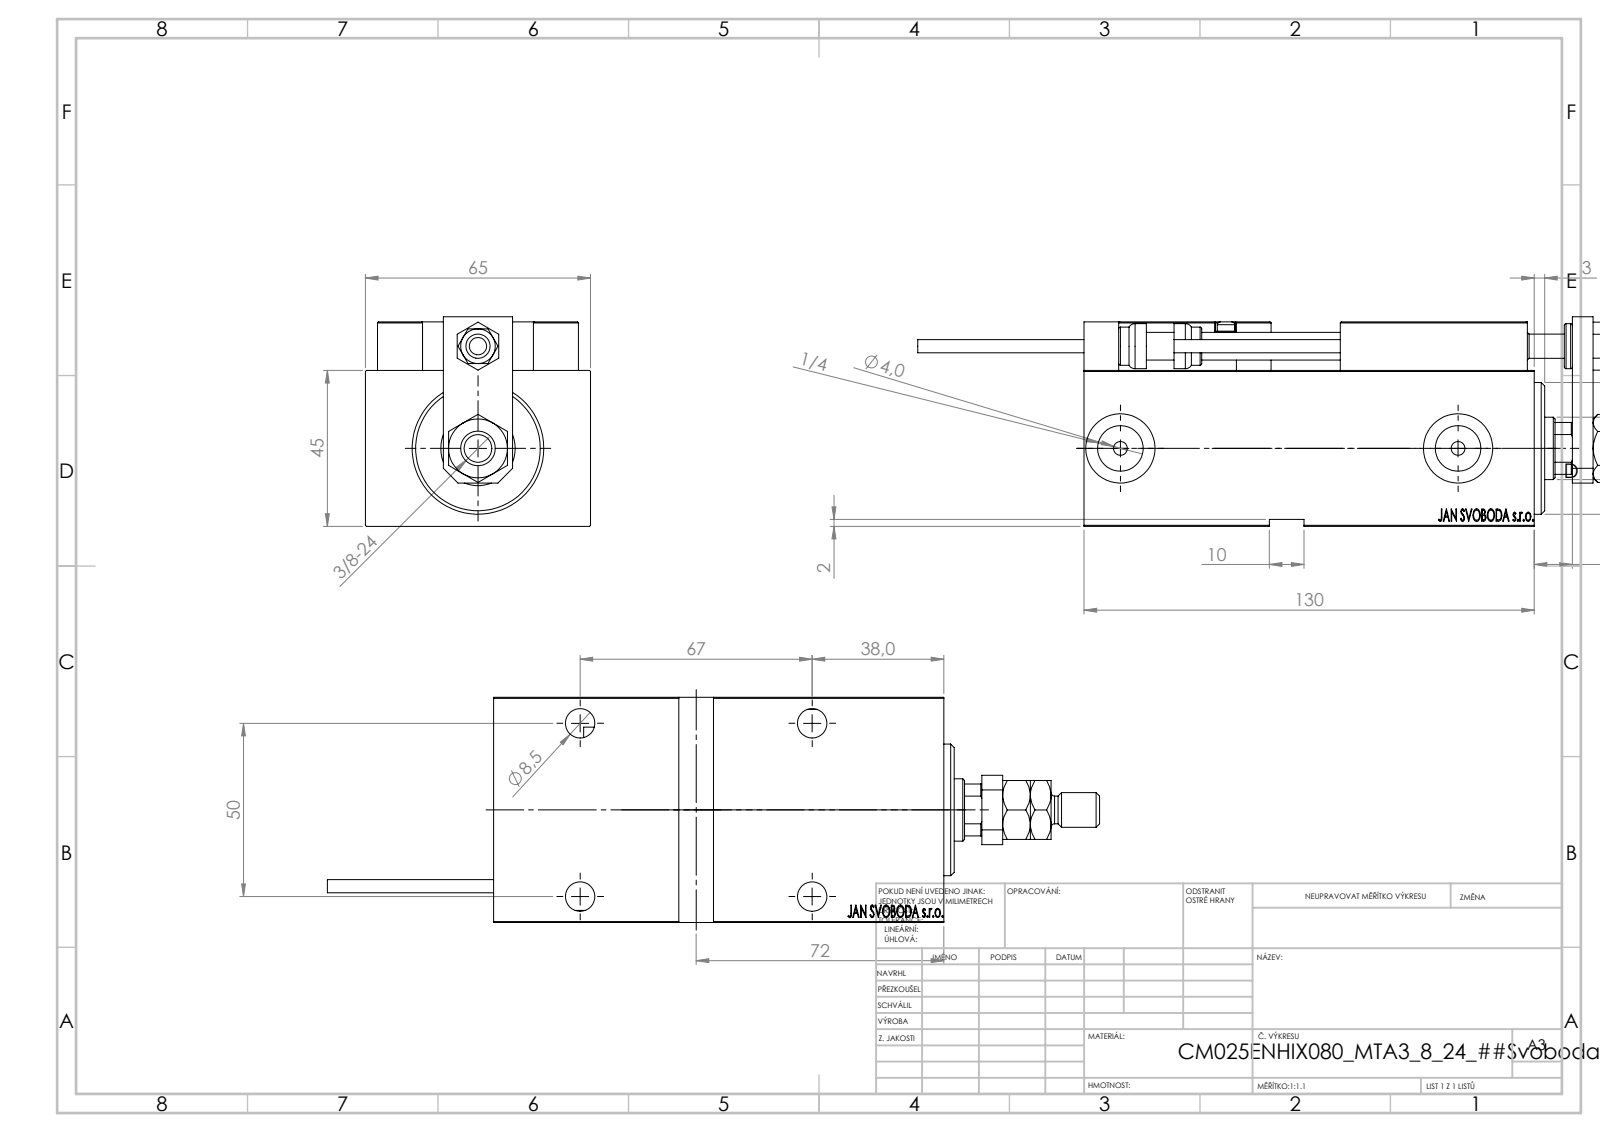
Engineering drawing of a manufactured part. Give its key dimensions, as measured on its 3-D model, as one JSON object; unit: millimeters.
{"part_name": "V450CM_E_VCP; Block; SWITCH DIM B,W; ALLEN BOLT D5 (+7 more)", "step_written_by": "SolidWorks 2019 (CONFIG_CONTROL_DESIGN)", "units": "millimeters", "bodies": {"solids": 25, "faces": 1342, "planar": 585, "cylindrical": 186, "other": 571}, "overall_size": [223, 65, 60.5], "volume_mm3": 400759, "surface_area_mm2": 91853, "round_holes": [[4, 6], [8, 5], [8.5, 5], [3.2, 4], [13.5, 4], [5, 2], [13.16, 2], [20, 2], [7, 1], [14.5, 1], [18, 1], [21.5, 1]], "round_bosses_or_shafts": [[5, 2], [3.8, 2], [38, 1], [27, 1], [13, 1], [11, 1], [10, 1], [8, 1]], "partial_cylinders_radius": [[0.3, 30], [3, 2], [8.5, 1]], "face_to_face_distances": [45, 65, 14, 6, 59, 130, 141, 13, 3.5, 19], "hole_center_spacings": [40.31, 11.37, 20, 25, 29.59, 29.69, 34.44, 36.06]}
